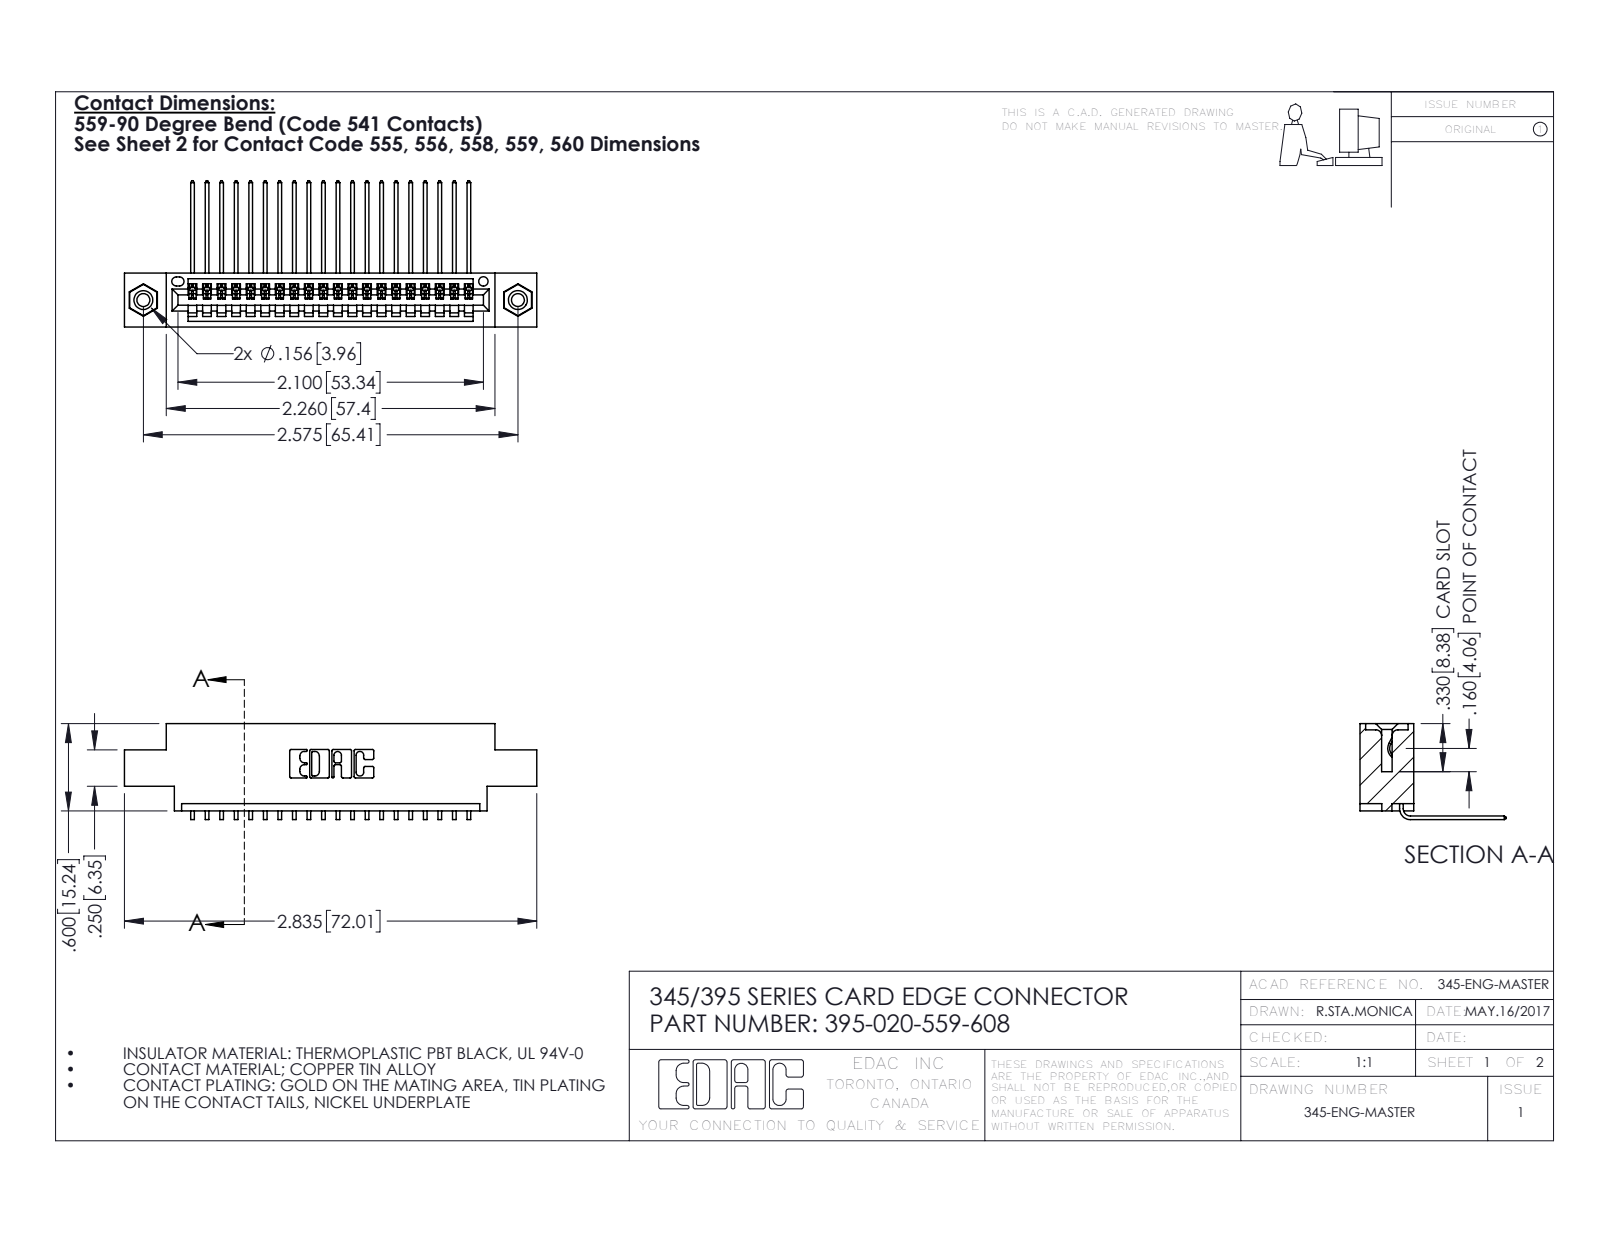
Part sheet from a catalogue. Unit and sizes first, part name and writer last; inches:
Units: inches
Overall size (bounding box): 2.835 × 1.005 × 0.659
Round holes (diameter × count): ⌀0.089 ×2, ⌀0.125 ×2, ⌀0.156 ×2, ⌀0.064 ×1
Round bosses / shafts (diameter × count): ⌀0.155 ×2
Partial cylindrical surfaces — rounded edges, fillets, slot ends (radius × count): R0.006 ×40, R0.01 ×22, R0.007 ×6, R0.031 ×6, R0.026 ×3, R0.031 ×2, R0.04 ×2, R0.014 ×1
Main face-to-face distances: 0.072, 0.298, 0.37, 0.2, 0.098, 0.272, 0.025, 0.225, 0.175, 0.15
Hole centre spacings: 0.27, 2.341, 2.575
Volume: 0.403 in³ · Surface area: 13.98 in²
Bodies: 23 solids, 1390 faces (956 planar, 418 cylindrical, 16 other)
Part name (STEP PRODUCT): 395-020-559-608; 345-250-001_345-250-003-102; 345 Part_0.170 Offset - 0.156 Dia-TI; 345-292-001_558 559 Tail - 1
STEP written by: SolidWorks 2016 (CONFIG_CONTROL_DESIGN)
